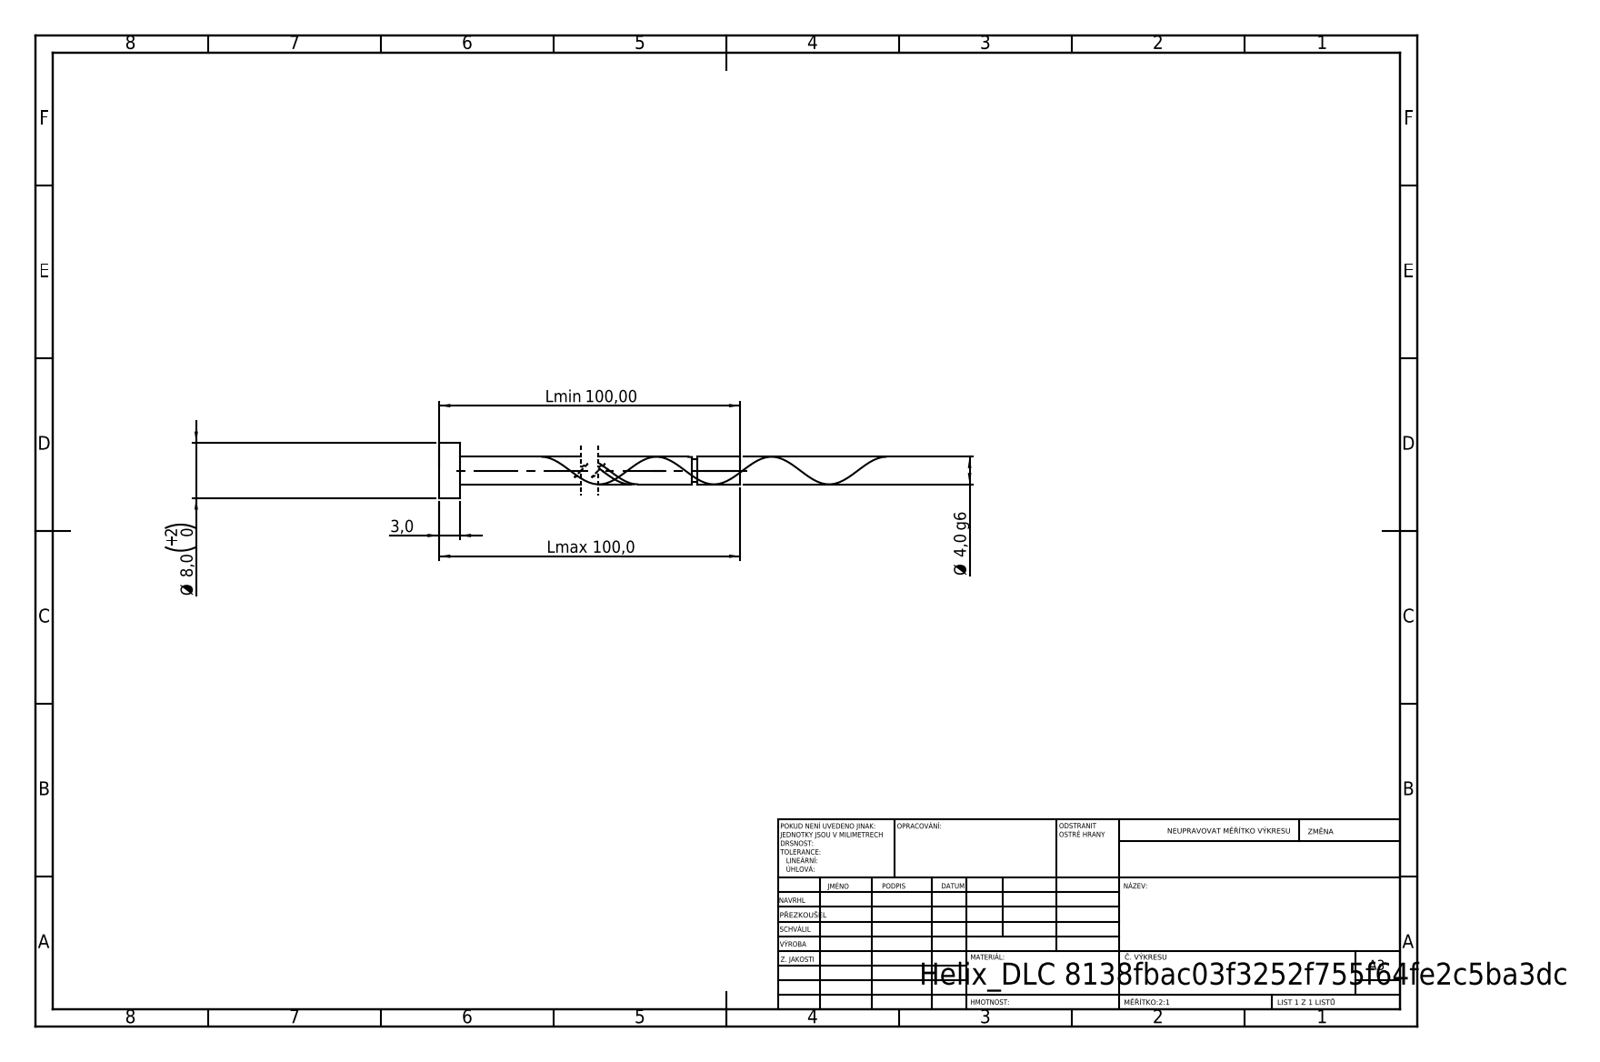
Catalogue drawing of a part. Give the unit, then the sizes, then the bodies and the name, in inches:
Units: inches
Overall size (bounding box): 3.937 × 0.315 × 0.315
Round bosses / shafts (diameter × count): ⌀0.315 ×1, ⌀0.157 ×1, ⌀0.126 ×1
Main face-to-face distances: 0.118, 3.937, 3.819, 3.693, 3.574, 0.244, 3.661, 3.543, 0.031, 0.276
Volume: 0.083 in³ · Surface area: 2.213 in²
Bodies: 1 solid, 21 faces (6 planar, 14 cylindrical, 1 other)
STEP written by: SolidWorks 2019 (CONFIG_CONTROL_DESIGN)
